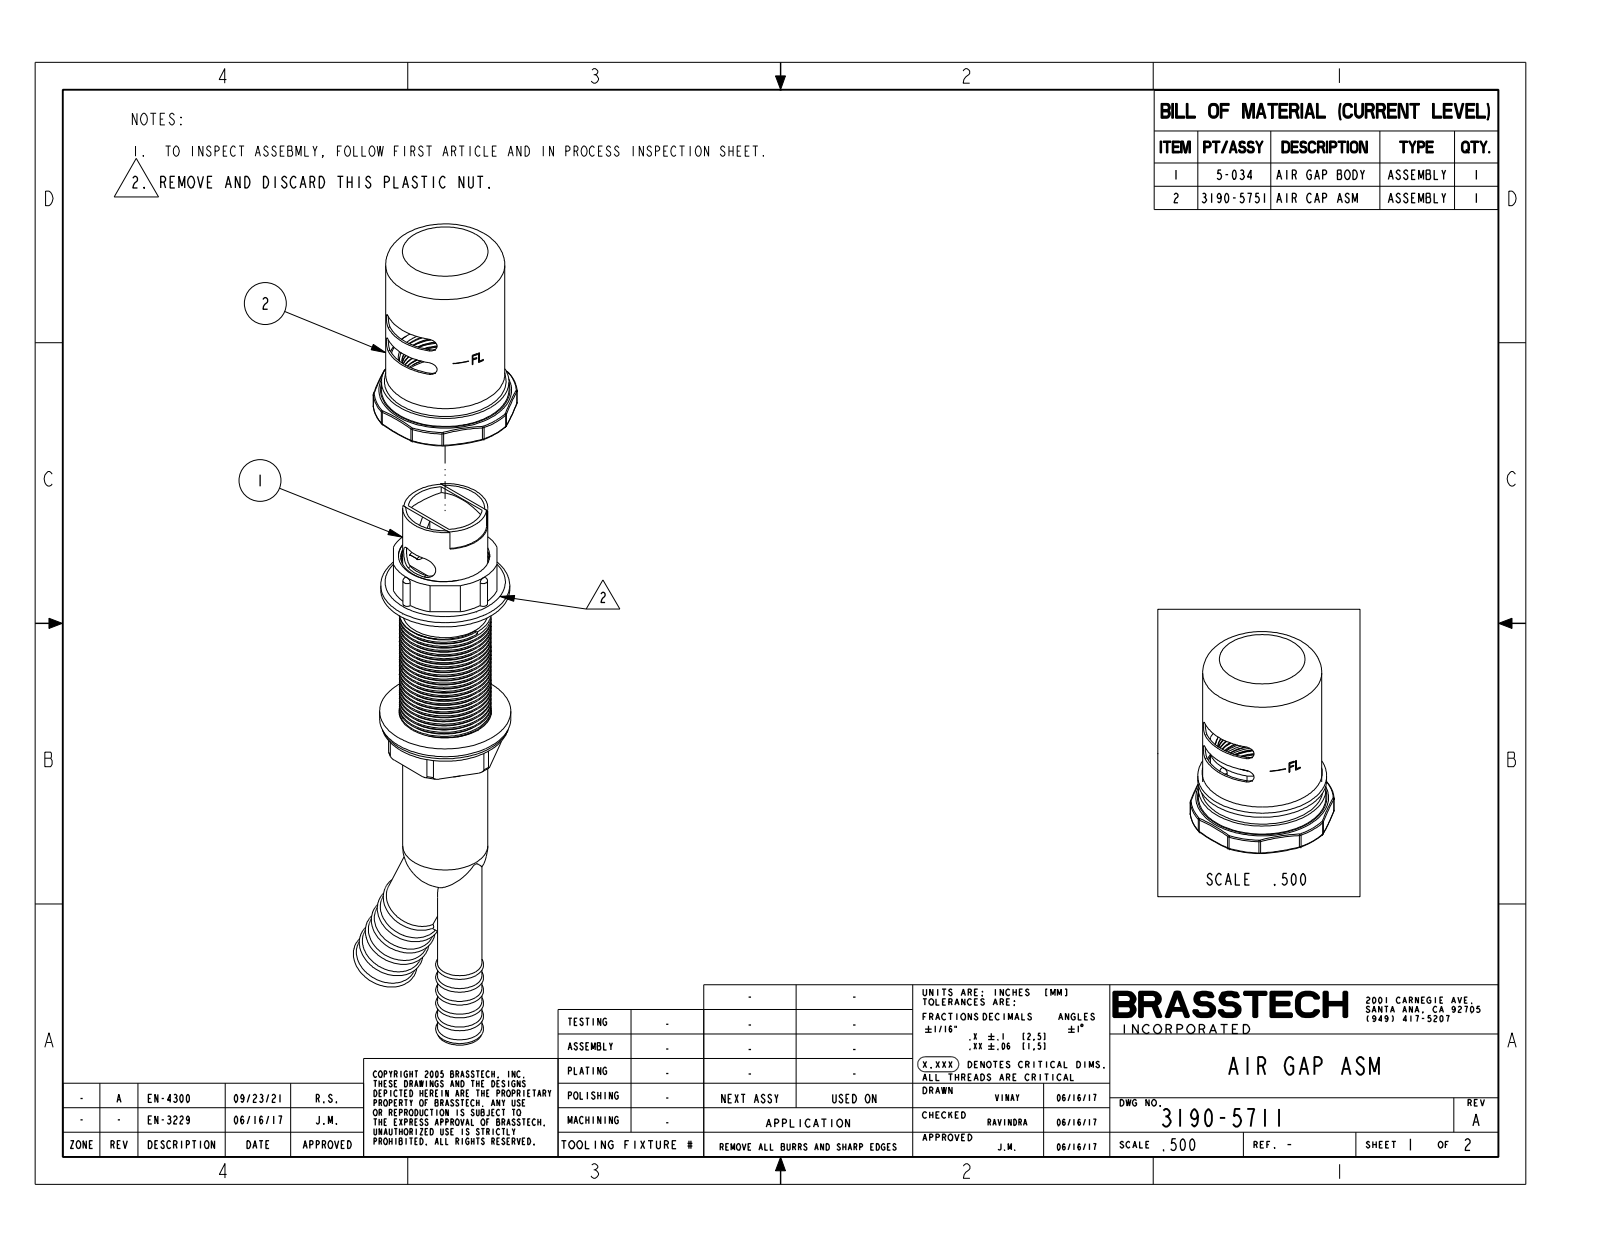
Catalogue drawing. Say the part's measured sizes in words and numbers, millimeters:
The part is named "3190-5711". Its 3-D file was written by "CREO PARAMETRIC BY PTC INC, 2018400 (AUTOMOTIVE_DESIGN)". It is 2 solids with 348 faces: 73 planar, 146 cylindrical and 129 other. Overall it measures 223.6 by 65.3 by 48 millimeters. Its volume is 164 700 cubic millimeters and its surface area 51 050 square millimeters. Round holes: 1 of diameter 30.5, 1 of diameter 32.3, 1 of diameter 32.5, 1 of diameter 40. Round bosses or shafts: 1 of diameter 45.7, 1 of diameter 44.7, 1 of diameter 44.5, 1 of diameter 41.5, 1 of diameter 32, 1 of diameter 29.7, 1 of diameter 21.7, 1 of diameter 15.5. Partial cylindrical surfaces (rounded edges, fillets, slot ends): 12 of radius 2, 6 of radius 1, 4 of radius 2.5, 2 of radius 4, 1 of radius 20.5, 1 of radius 25.1. The main face-to-face distances are 23.4, 34.2, 10.8, 89, 89.8, 65.7, 66.4, 54.9, 55.6, 0.8.
